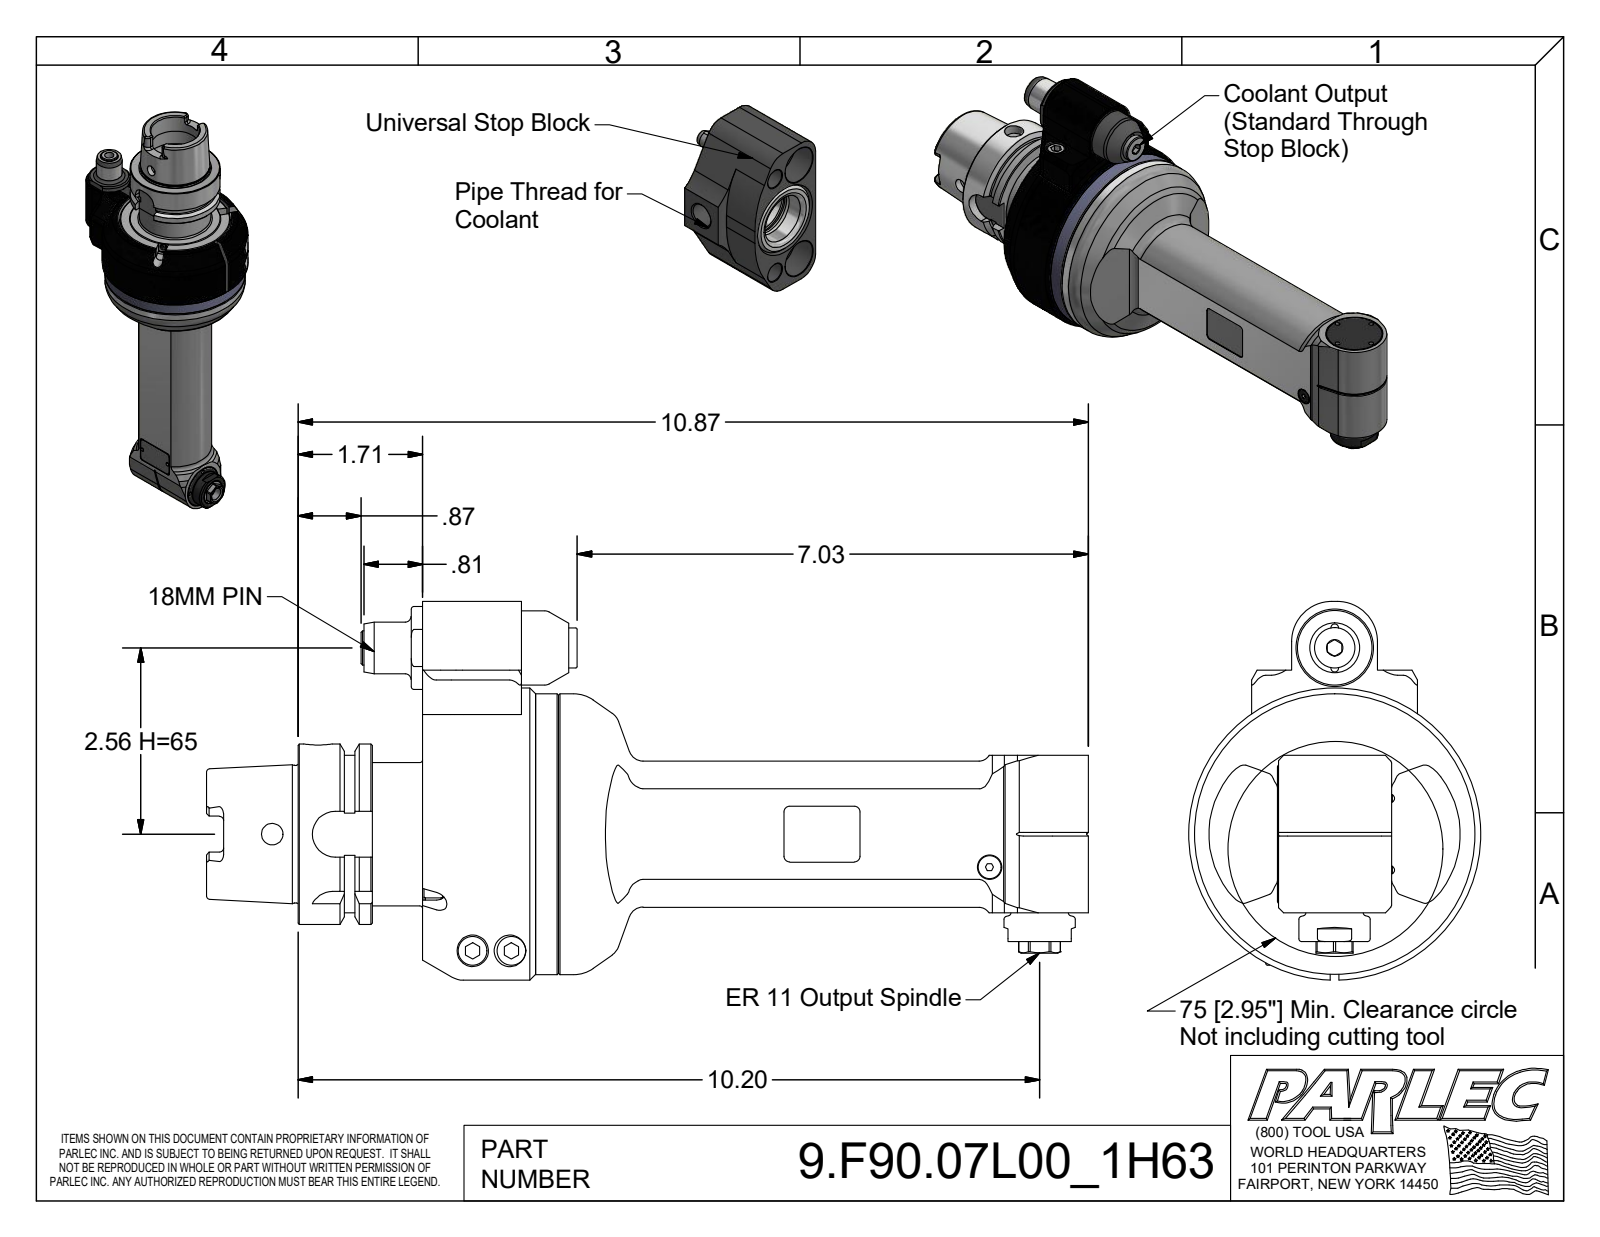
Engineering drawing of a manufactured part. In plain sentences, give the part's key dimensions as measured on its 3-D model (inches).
The part is named "9FL1ATC; 9HSK631ATC; 9F18T165A; 9F18T100 (+4 more)". Its 3-D file was written by "Autodesk Inventor 2016 (AUTOMOTIVE_DESIGN)". It is 4 solids with 558 faces: 264 planar, 138 cylindrical and 156 other. Overall it measures 12.126 by 5.206 by 4.016 inches. Its volume is 50.14 cubic inches and its surface area 223.5 square inches. Round holes: 6 of diameter 0.102, 2 of diameter 0.165, 2 of diameter 0.197, 2 of diameter 0.295, 2 of diameter 0.409, 2 of diameter 0.433, 2 of diameter 0.492, 1 of diameter 0.098, 1 of diameter 0.118, 1 of diameter 0.256, 1 of diameter 0.276, 1 of diameter 0.335. Round bosses or shafts: 4 of diameter 0.394, 4 of diameter 0.236, 3 of diameter 0.709, 2 of diameter 0.315, 2 of diameter 0.098, 1 of diameter 4.016, 1 of diameter 3.858, 1 of diameter 3.031. Partial cylindrical surfaces (rounded edges, fillets, slot ends): 12 of radius 0.079, 6 of radius 0.059, 4 of radius 0.113, 4 of radius 0.157, 4 of radius 0.315, 2 of radius 0.016, 2 of radius 0.02, 2 of radius 0.039. The main face-to-face distances are 1.26, 1.575, 0.276, 1.024, 1.555, 0.02, 0.295, 0.197, 0.335, 0.984. The hole center spacings are 0.492, 0.696, 0.276, 0.984, 9.933, 0.014, 0.478, 0.506.
